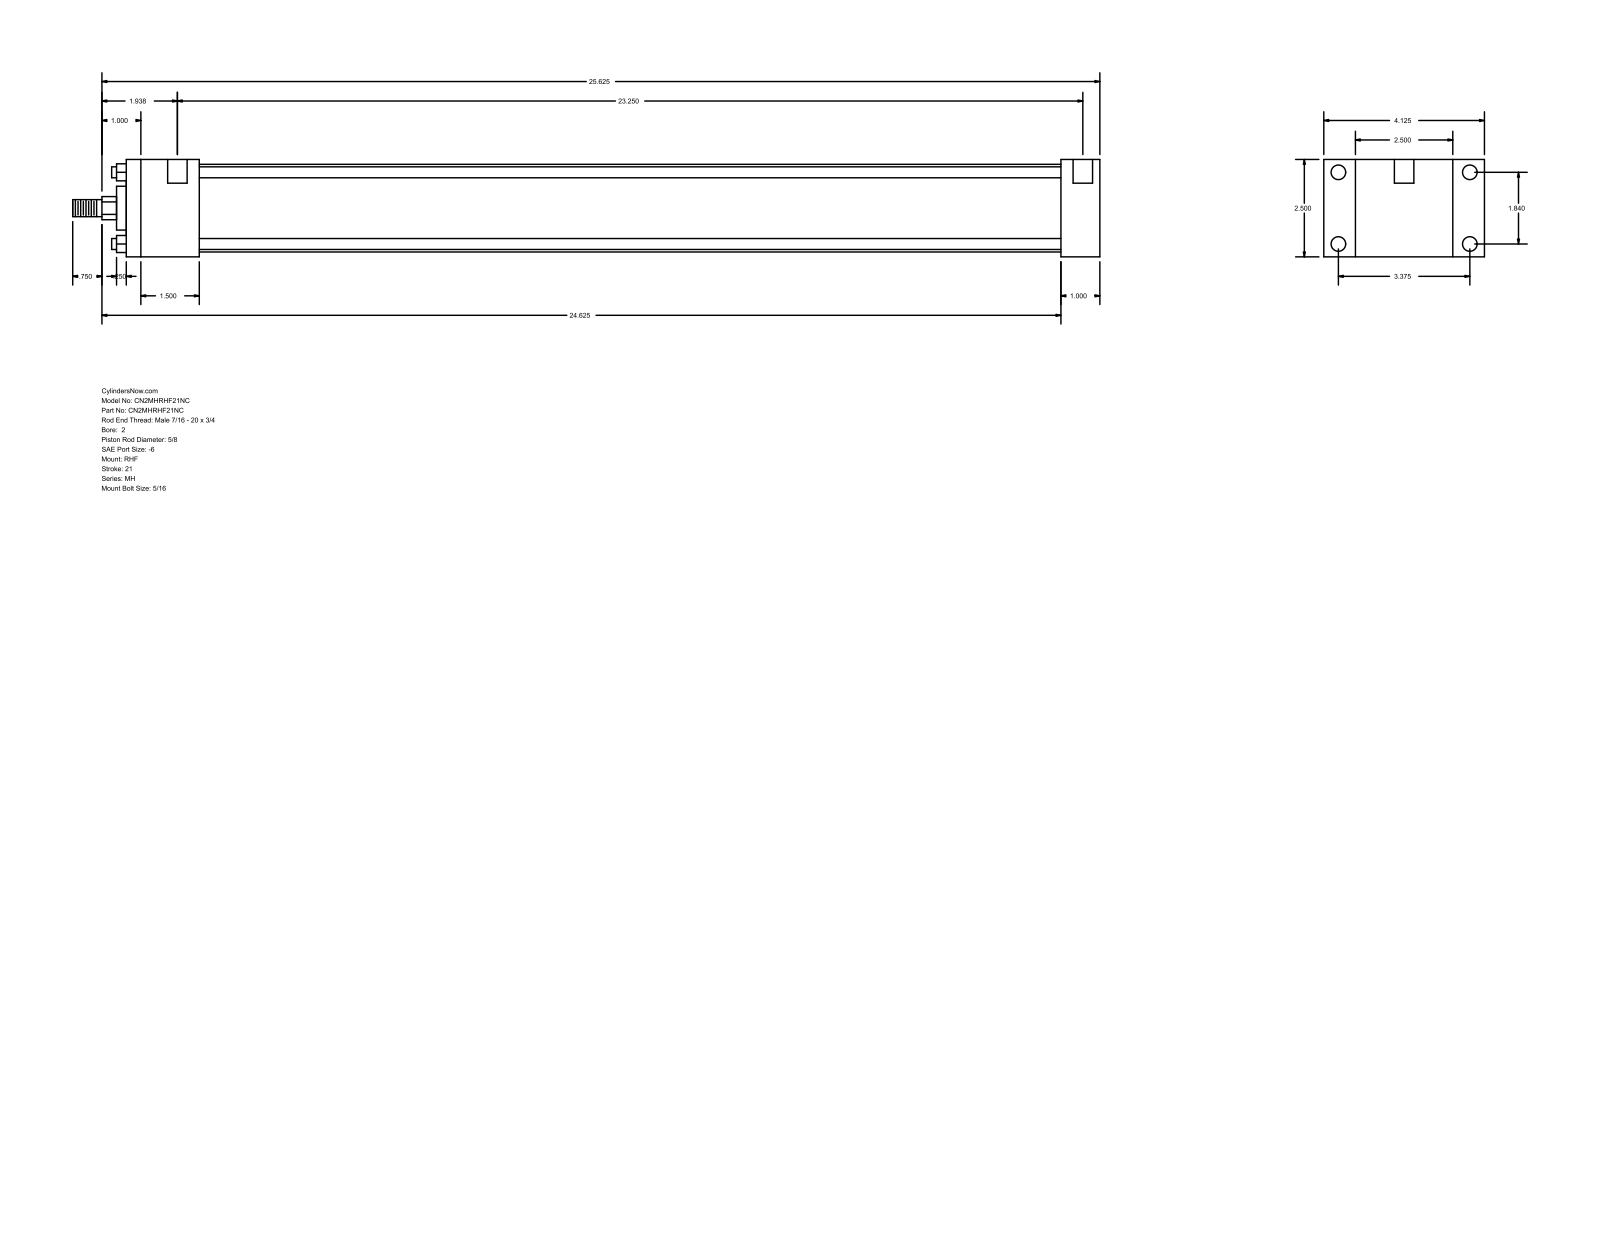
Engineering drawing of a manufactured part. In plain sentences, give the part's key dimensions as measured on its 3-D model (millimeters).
The part is named "MH_RHF__0200_0.625". Its 3-D file was written by "GSSL Pune (CONFIG_CONTROL_DESIGN)". It is 0 solids with 88 faces: 60 planar, 28 cylindrical and 0 other. Overall it measures 669.92 by 104.78 by 63.5 millimeters. Round holes: 4 of diameter 5.56, 4 of diameter 9.53, 2 of diameter 12.7. Round bosses or shafts: 4 of diameter 7.14, 1 of diameter 57.15, 1 of diameter 28.57, 1 of diameter 15.88, 1 of diameter 11.11. Partial cylindrical surfaces (rounded edges, fillets, slot ends): 1 of radius 7.54. The main face-to-face distances are 63.5, 25.4, 20.64, 84.14, 609.6, 635, 104.78, 47.62, 561.98, 587.38. The hole center spacings are 46.74, 85.72, 97.63, 598.49, 3.18, 4.76, 590.55, 593.73.
